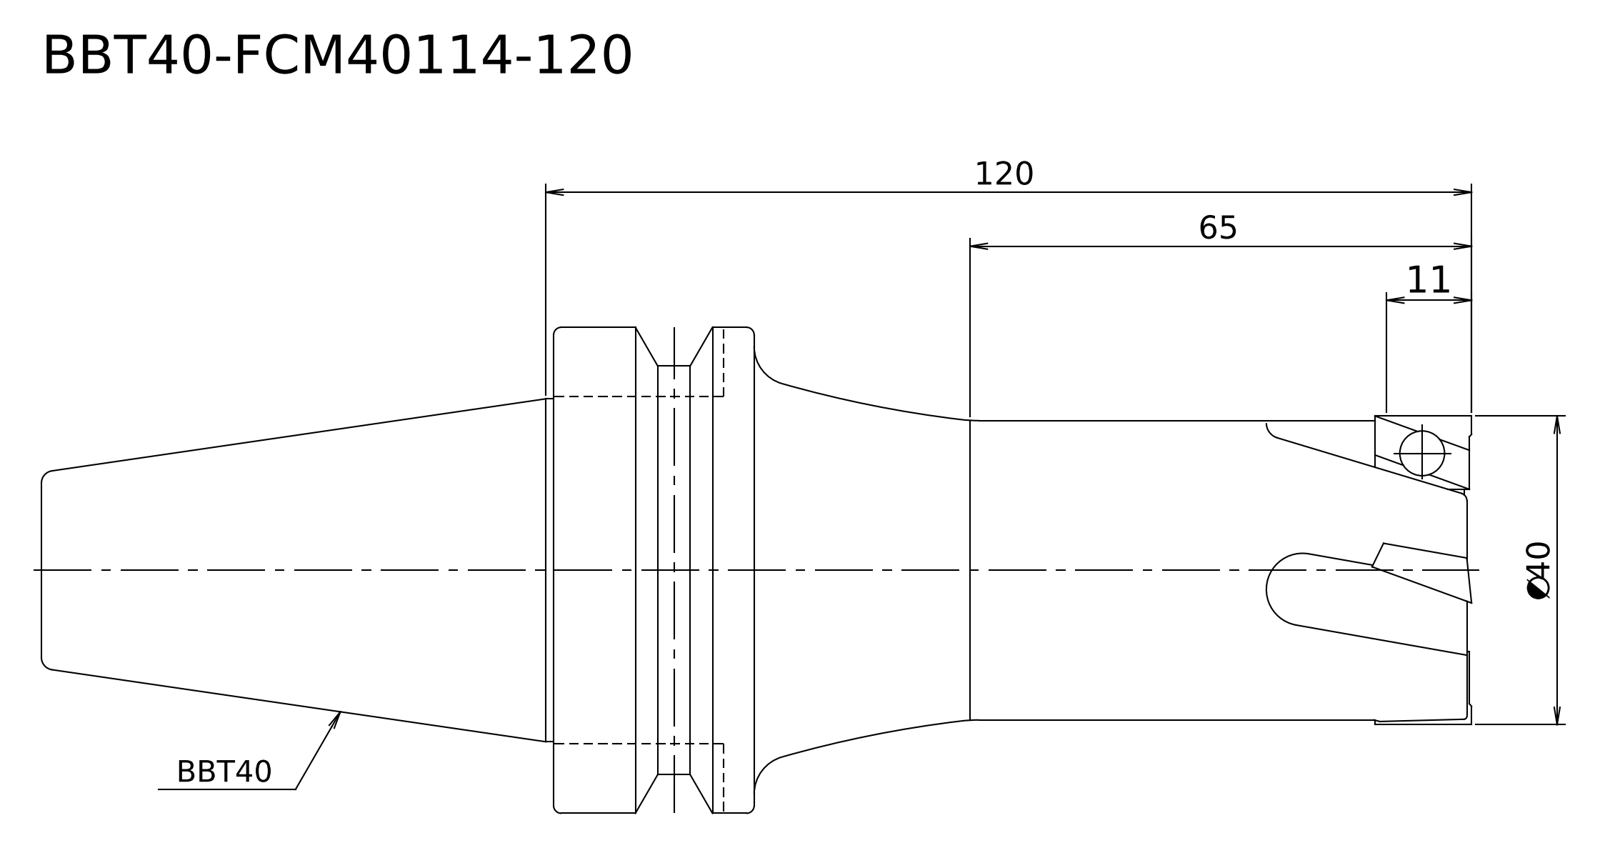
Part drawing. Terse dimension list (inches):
written by: Kubotek KeyCreator V8.5.1 (14335) (CONFIG_CONTROL_DESIGN)
unit: in
bodies: 1 solid, 17 faces (4 planar, 6 cylindrical, 7 other)
size: 7.299 × 2.48 × 2.48
volume: 15.95 in³; area: 45.73 in²
bosses: 1× ⌀2.48, 1× ⌀2.087, 1× ⌀1.75, 1× ⌀1.575, 1× ⌀1.528
face distances: 4.685, 7.299, 2.614, 3.661, 1.024, 3.638
